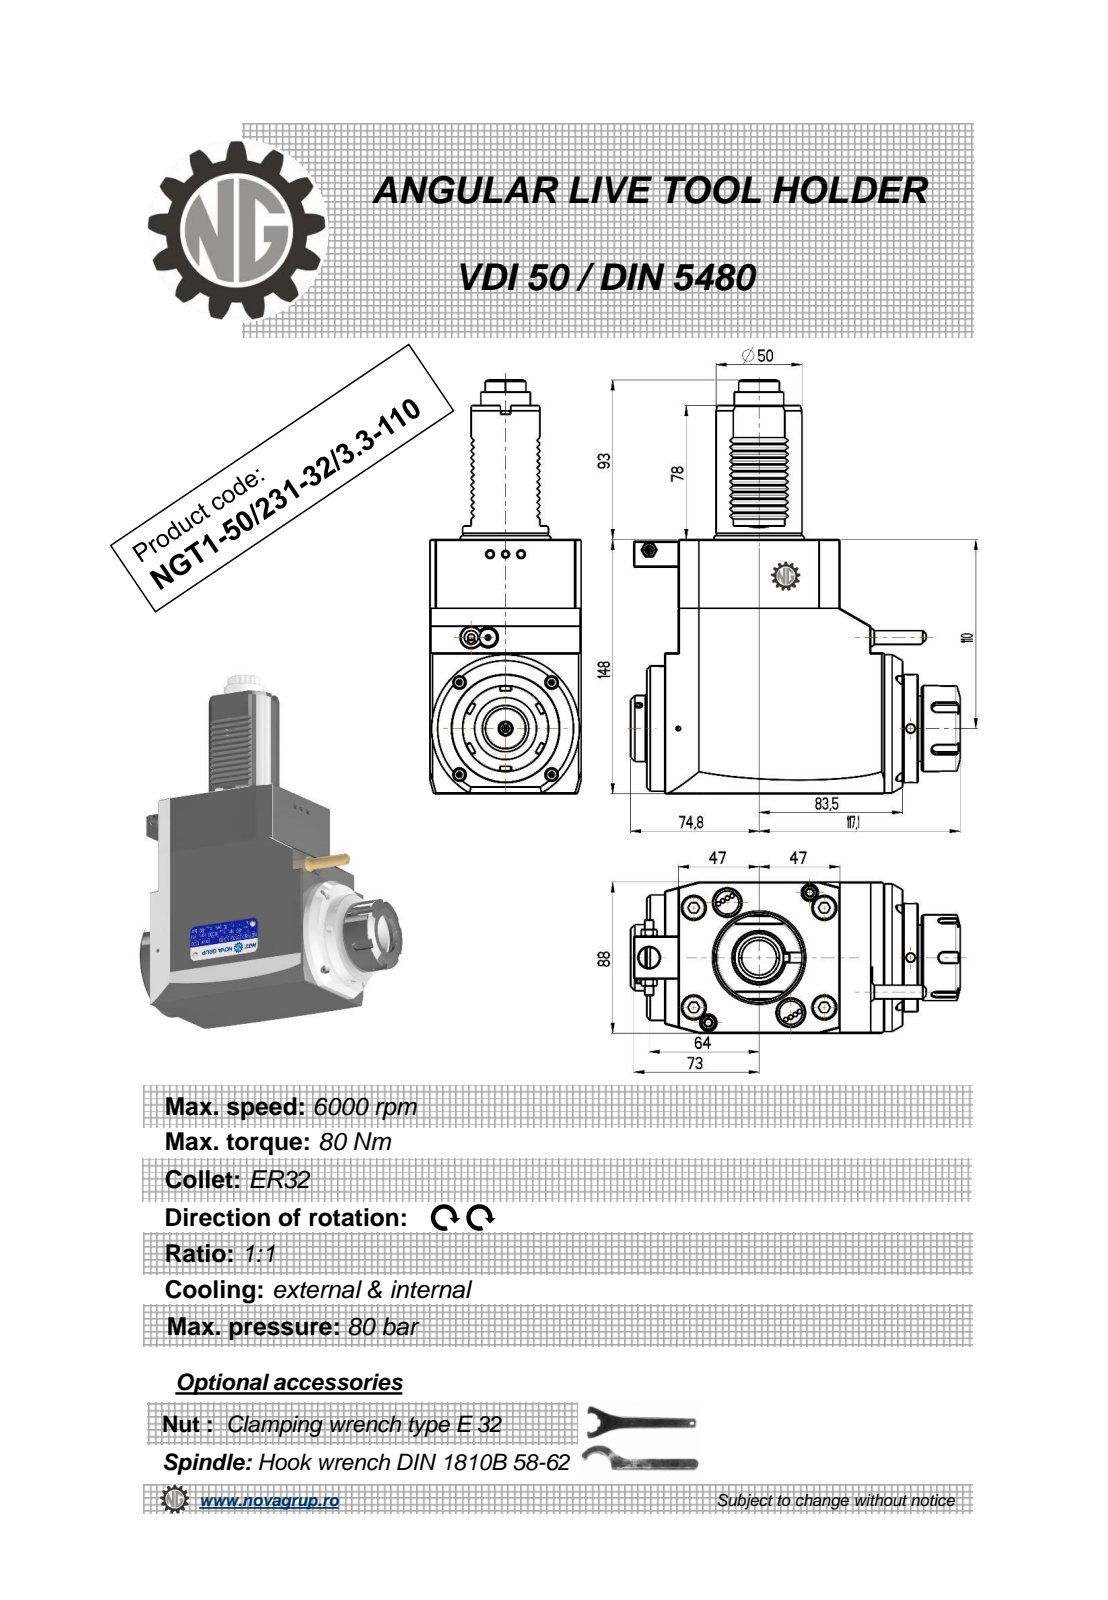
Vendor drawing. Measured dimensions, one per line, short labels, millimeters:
name: NGT1_50_231_32_3_3_110
written by: PRO/ENGINEER BY PARAMETRIC TECHNOLOGY CORPORATION, 2010280 (CONFIG_CONTROL_DESIGN)
unit: mm
bodies: 1 solid, 568 faces (236 planar, 173 cylindrical, 159 other)
size: 241 × 191.9 × 88
volume: 1 818 000 mm³; area: 113 531 mm²
holes: 3× ⌀5, 1× ⌀3, 1× ⌀4.2, 1× ⌀9.5, 1× ⌀12, 1× ⌀27
bosses: 2× ⌀50, 1× ⌀86, 1× ⌀73, 1× ⌀63, 1× ⌀50.5, 1× ⌀41, 1× ⌀40, 1× ⌀38.5
rounds: 36× R3.04, 24× R0.3, 12× R0.26, 6× R0.2, 5× R3, 1× R10.56, 1× R11.88, 1× R17.5
face distances: 88, 148, 94, 8, 120, 36.5, 130.5, 18.3, 112.3, 148.8
hole spacings: 52.46, 56.65, 101.5, 152.25, 184.38
